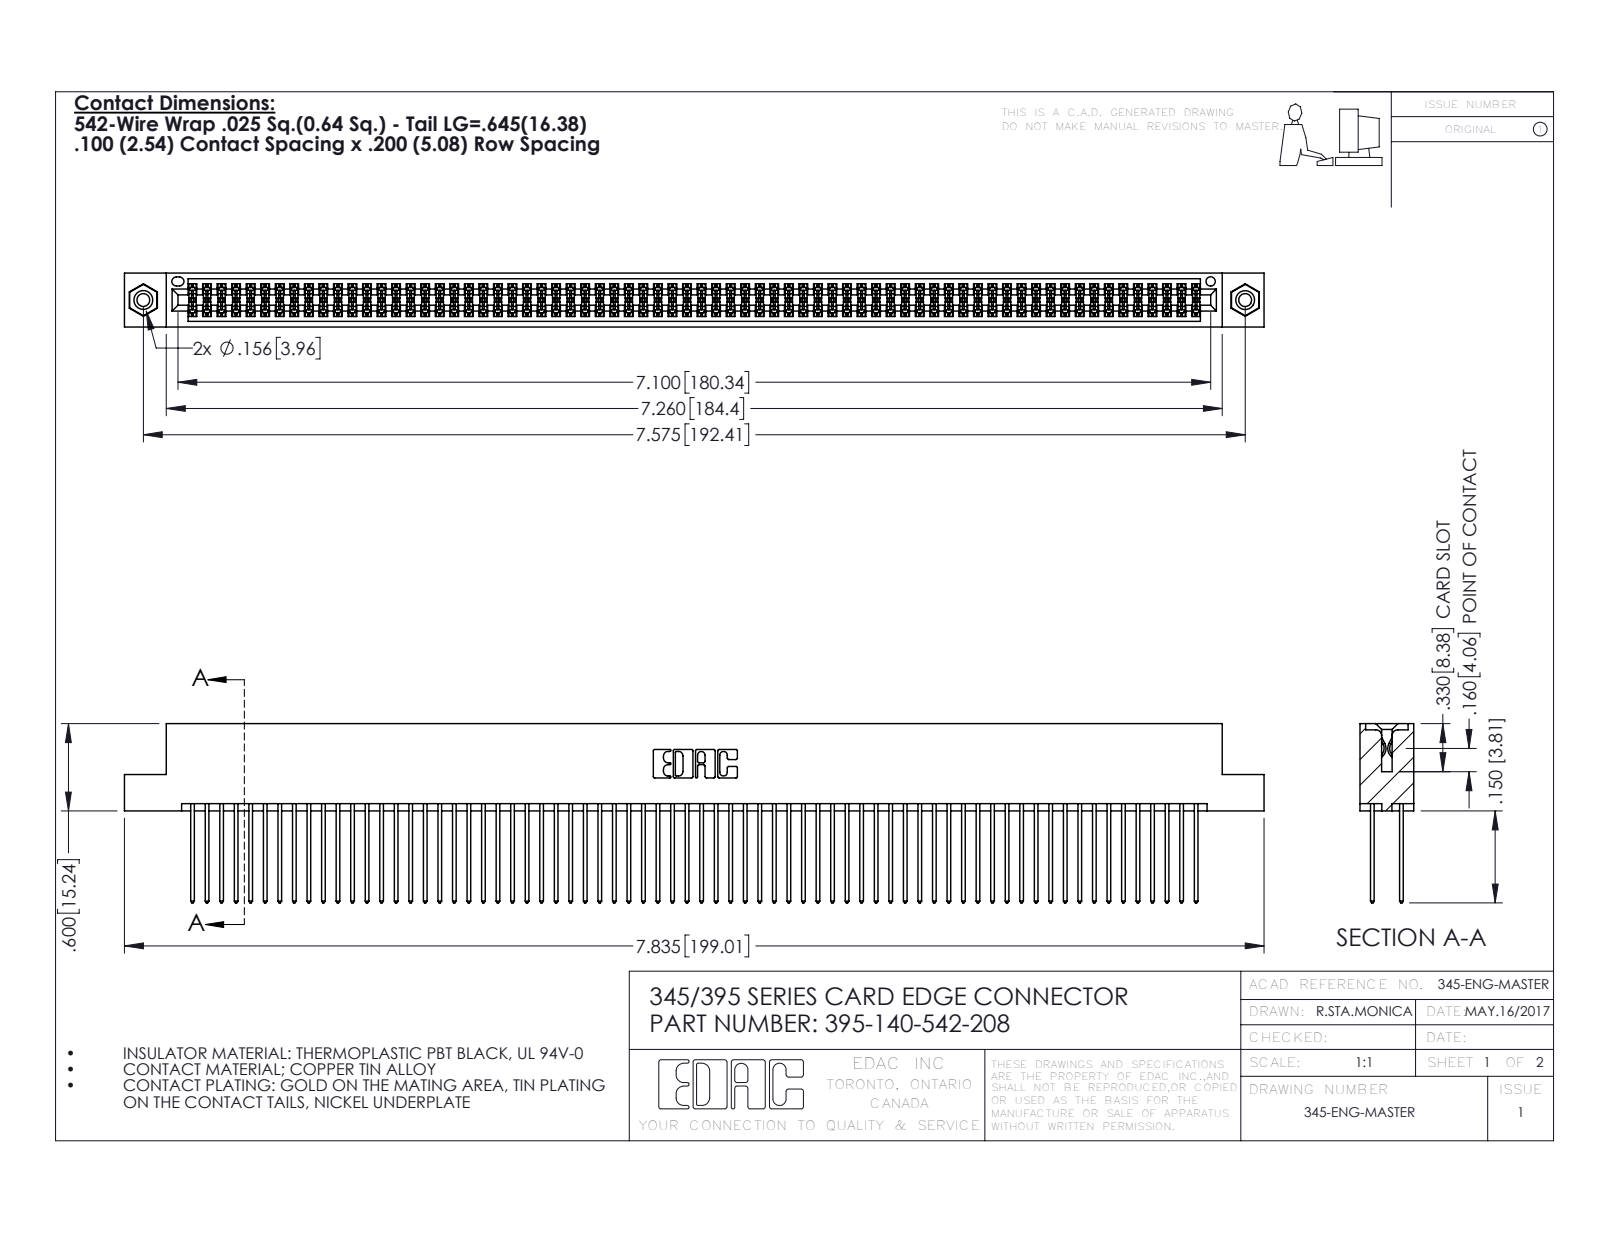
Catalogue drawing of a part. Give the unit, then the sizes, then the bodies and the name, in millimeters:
Units: millimetres
Overall size (bounding box): 199 × 31.3 × 9.4
Round holes (diameter × count): ⌀2.3 ×2, ⌀3.2 ×2, ⌀4 ×2, ⌀1.6 ×1
Round bosses / shafts (diameter × count): ⌀3.9 ×2
Partial cylindrical surfaces — rounded edges, fillets, slot ends (radius × count): R0.2 ×210, R0.3 ×140, R0.3 ×22, R0.2 ×6, R0.8 ×6, R0.7 ×3, R0.4 ×2, R0.5 ×2
Main face-to-face distances: 1.8, 7.6, 5.1, 2.5, 6.9, 0.6, 5.7, 9.4, 4.4, 3.8
Hole centre spacings: 6.9, 186.4, 192.4
Volume: 20 240 mm³ · Surface area: 33 520 mm²
Bodies: 143 solids, 7186 faces (4732 planar, 2438 cylindrical, 16 other)
Part name (STEP PRODUCT): 345 Part_Flush Mounting Lugs - 0.156 Dia-TI; 345-250-001_345-250-003-102; 345-292-001_345-293-142; 395-140-542-208
STEP written by: SolidWorks 2016 (CONFIG_CONTROL_DESIGN)
